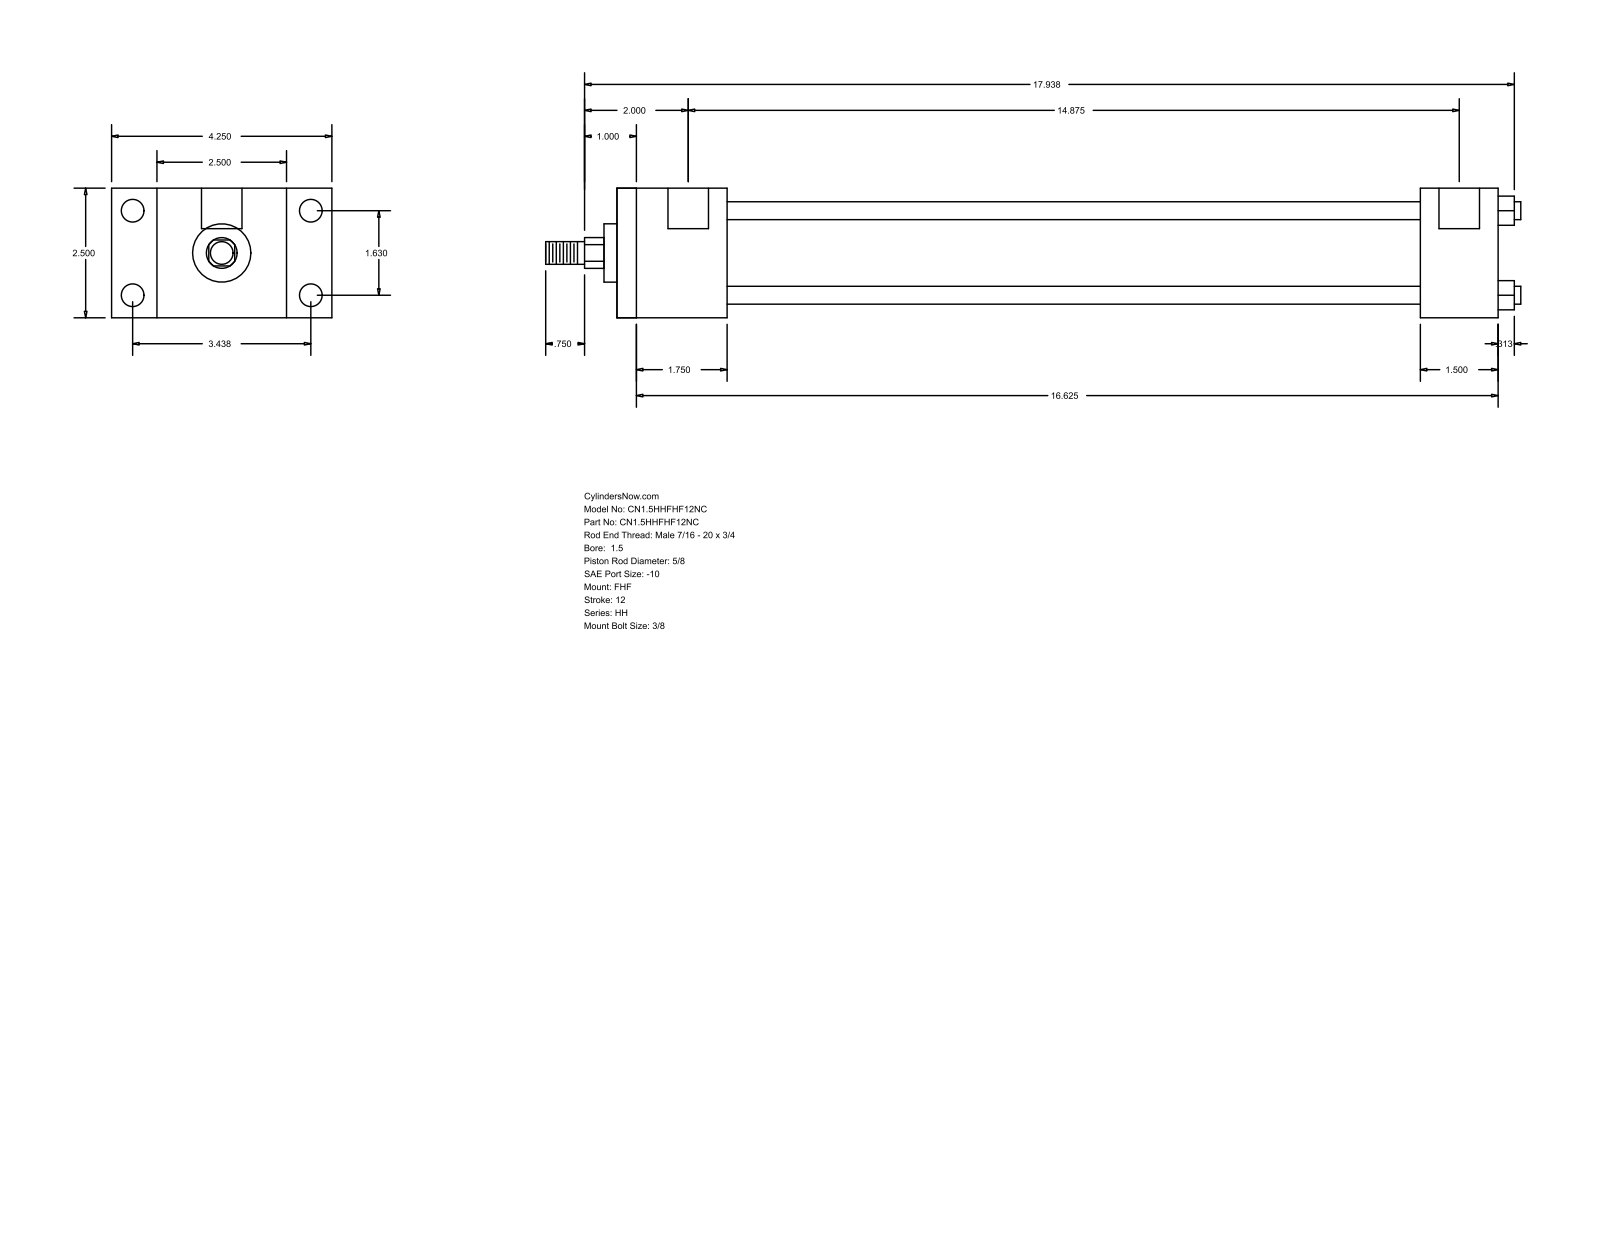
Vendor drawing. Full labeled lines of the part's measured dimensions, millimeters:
Part name (STEP PRODUCT): HH_FHF__0150_0.625
STEP written by: GSSL Pune (CONFIG_CONTROL_DESIGN)
Units: millimetres
Bodies: 0 solids, 88 faces (60 planar, 28 cylindrical, 0 other)
Overall size (bounding box): 477.84 × 107.95 × 63.5
Round holes (diameter × count): ⌀5.56 ×4, ⌀11.13 ×4, ⌀19.84 ×2
Round bosses / shafts (diameter × count): ⌀8.76 ×4, ⌀44.45 ×1, ⌀28.57 ×1, ⌀15.88 ×1, ⌀11.11 ×1
Partial cylindrical surfaces — rounded edges, fillets, slot ends (radius × count): R7.54 ×1
Main face-to-face distances: 63.5, 22.23, 85.73, 53.97, 107.96, 431.8, 377.83, 393.69, 339.72, 38.11
Hole centre spacings: 1.59, 41.4, 87.32, 96.64, 379.41, 381, 377.82
